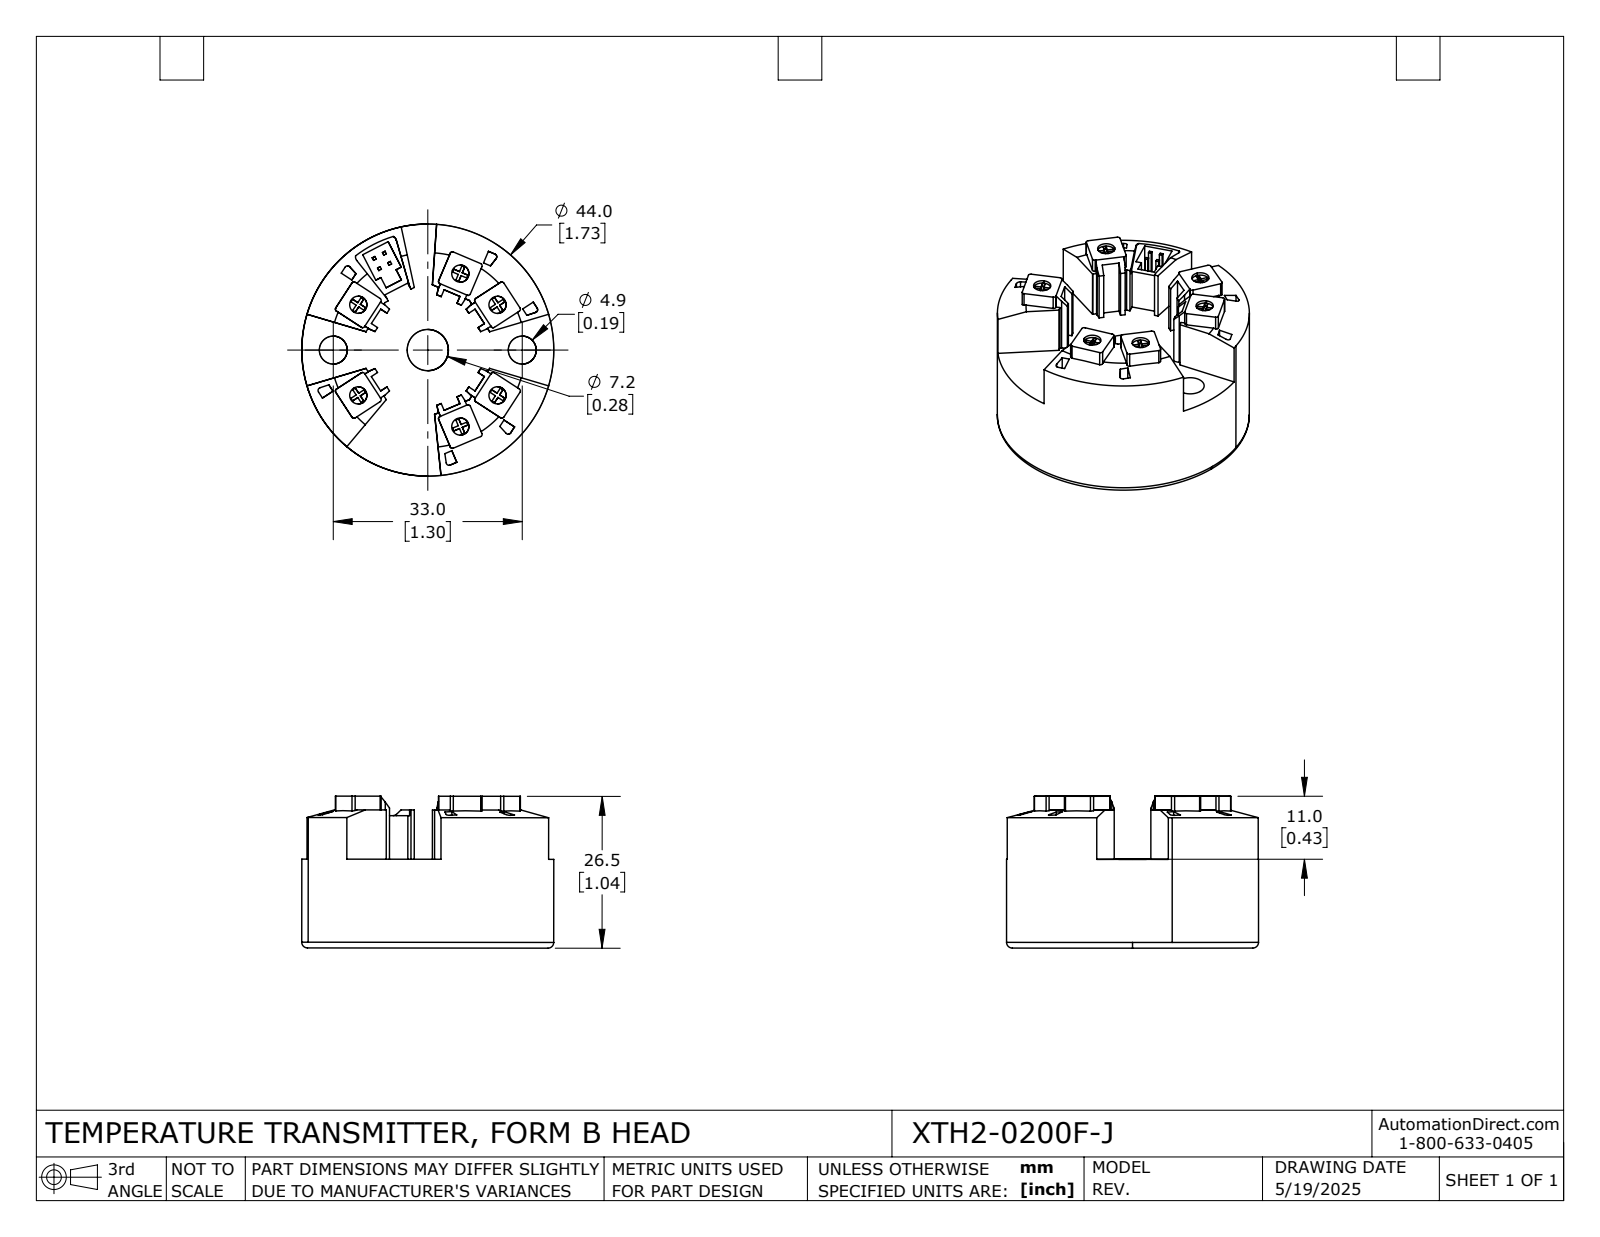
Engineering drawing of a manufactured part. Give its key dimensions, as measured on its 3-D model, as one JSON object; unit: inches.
{"part_name": "XTDH2-0200F-J", "step_written_by": "SolidWorks 2024 (AUTOMOTIVE_DESIGN)", "units": "inches", "bodies": {"solids": 1, "faces": 341, "planar": 281, "cylindrical": 52, "other": 8}, "overall_size": [1.733, 1.732, 1.045], "volume_in3": 1.748, "surface_area_in2": 13.46, "round_holes": [[0.118, 6], [0.193, 2], [0.283, 1]], "round_bosses_or_shafts": [[1.732, 1]], "partial_cylinders_radius": [[0.016, 24], [0.02, 6], [0.039, 2]], "face_to_face_distances": [0.61, 1.043, 0.433, 0.059, 0.177, 0.039, 0.02, 0.118, 0.949, 0.339], "hole_center_spacings": [0.571, 0.333, 0.355, 0.356, 0.65, 0.677, 0.733, 0.875]}
